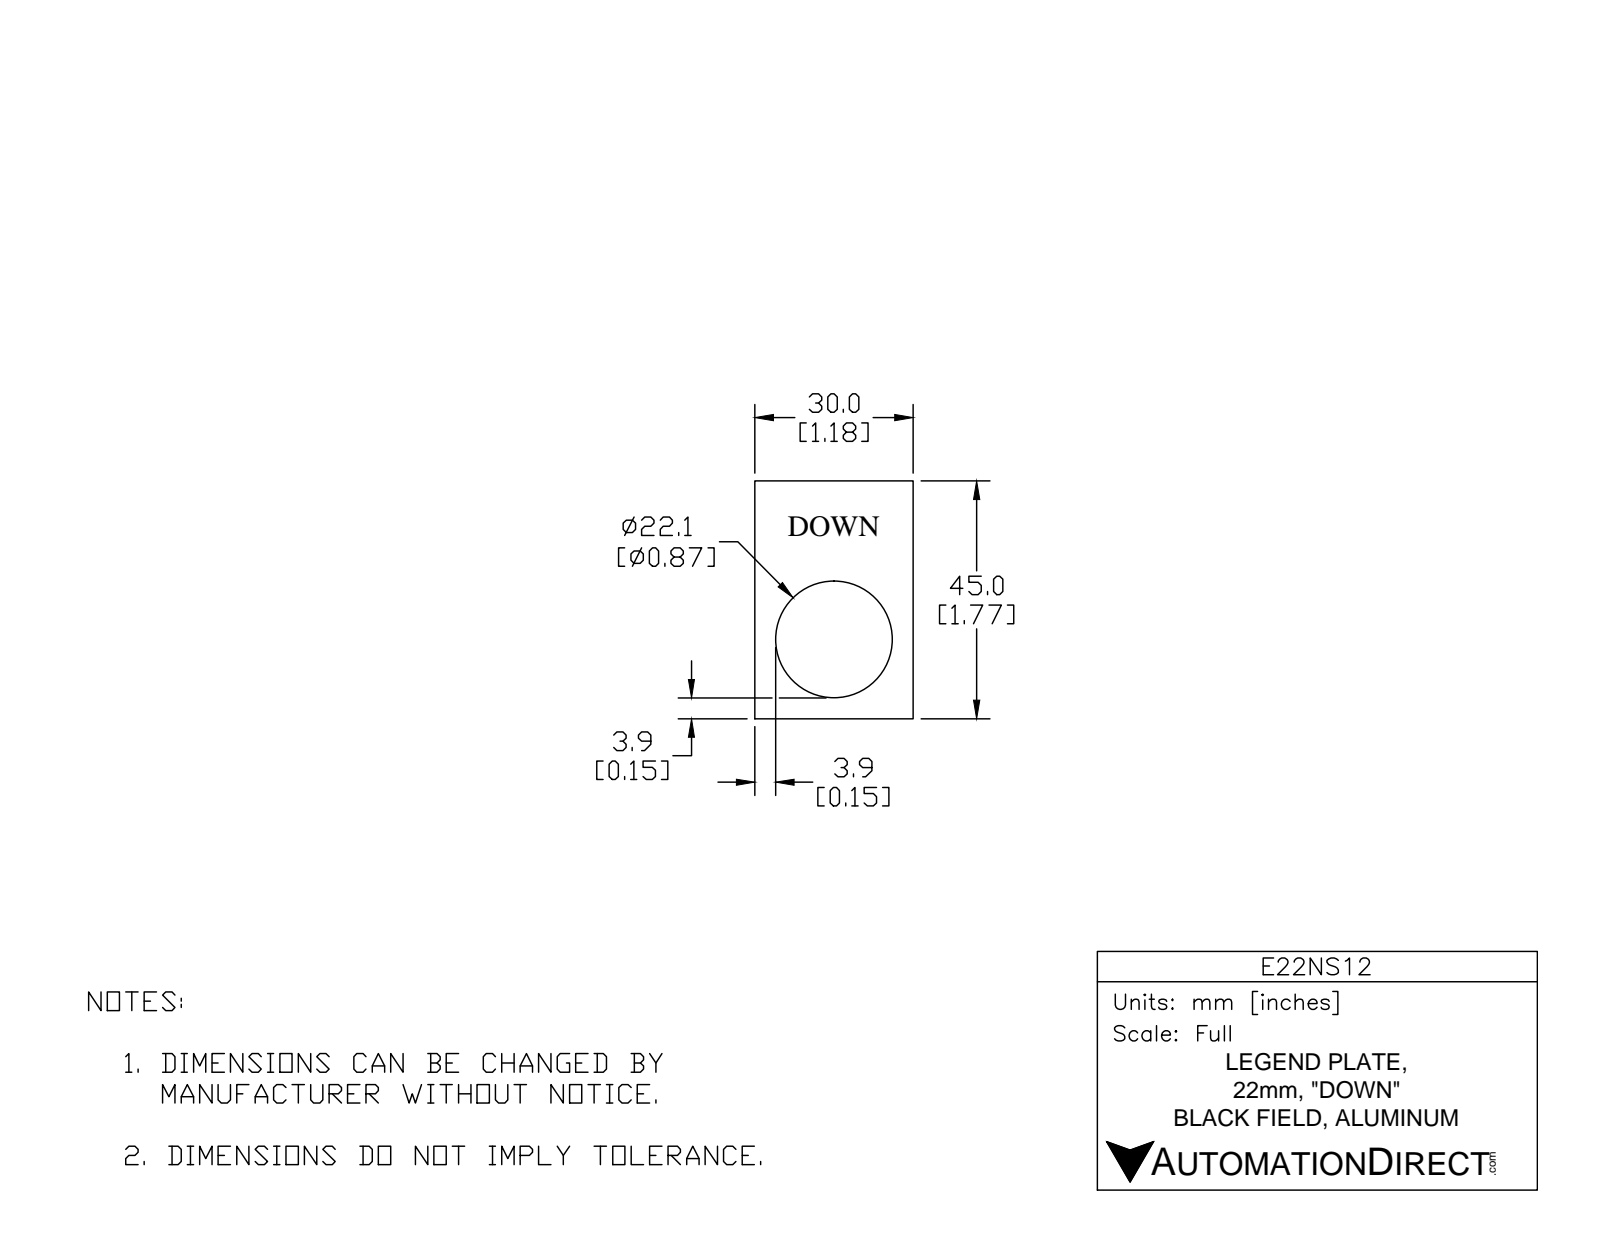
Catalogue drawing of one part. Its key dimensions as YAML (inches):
part_name: "E22NS12"
step_written_by: "SolidWorks 2017 (AUTOMOTIVE_DESIGN)"
units: inches
bodies: {solids: 1, faces: 62, planar: 44, cylindrical: 3, other: 15}
overall_size: [1.772, 1.181, 0.051]
volume: 0.076
surface_area: 3.477
round_holes:
  - {diameter: 0.874, count: 1}
face_to_face_distances: [0.051, 1.181, 1.772, 0.041, 0.185, 1.587, 0.254, 0.928, 0.528, 0.654]
